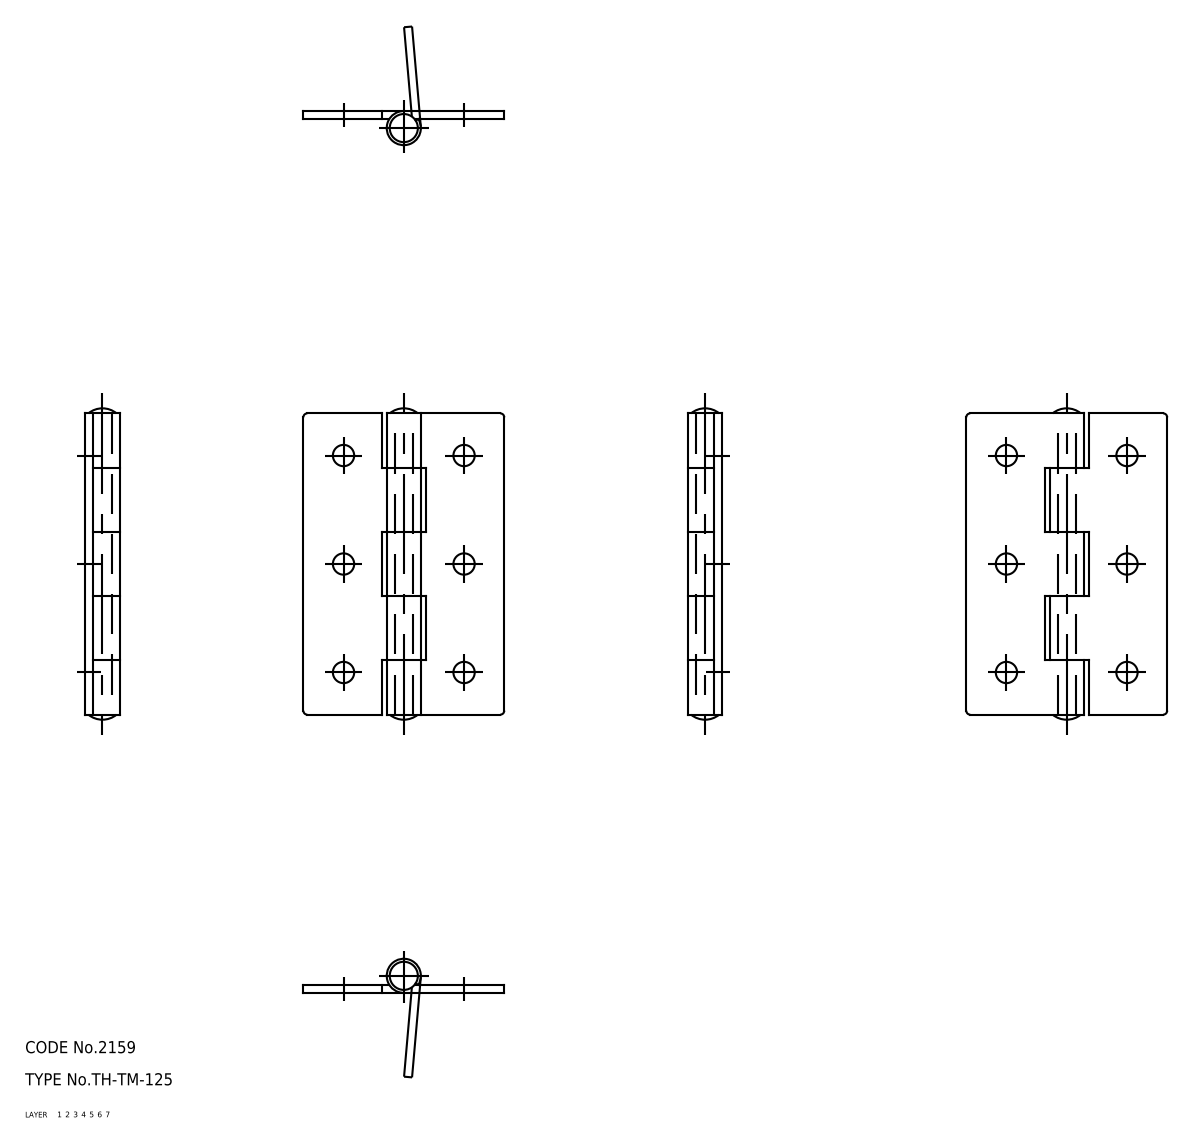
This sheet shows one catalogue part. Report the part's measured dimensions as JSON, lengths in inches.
{"part_name": "hinge piece_B; hinge piece_A; shaft; TH_TM_125_21608_36", "step_written_by": "CADfix (AUTOMOTIVE_DESIGN)", "units": "inches", "bodies": {"solids": 3, "faces": 60, "planar": 0, "cylindrical": 0, "other": 60}, "overall_size": [3.051, 1.969, 0.335], "volume_in3": 0.623, "surface_area_in2": 17.93}
